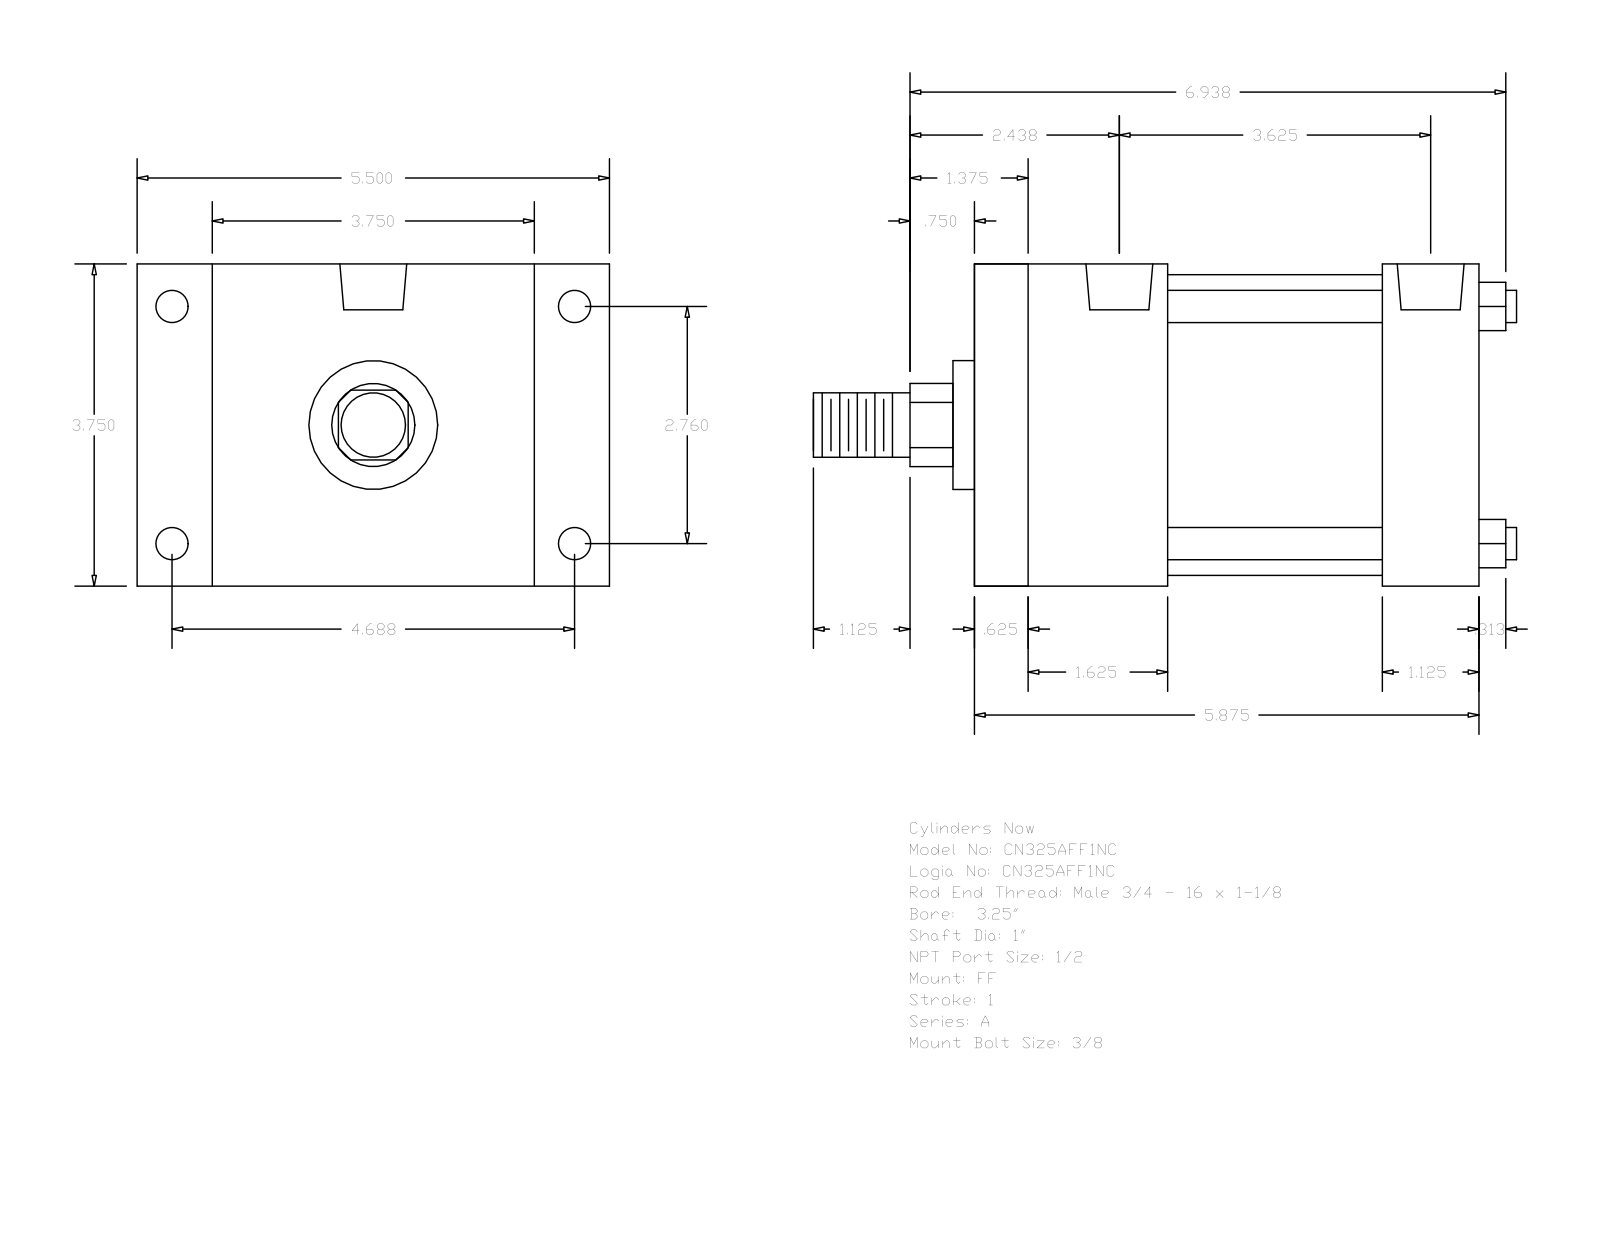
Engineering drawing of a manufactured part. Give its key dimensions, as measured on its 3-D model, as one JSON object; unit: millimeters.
{"part_name": "A_FF__0325_1", "step_written_by": "GSSL Pune (CONFIG_CONTROL_DESIGN)", "units": "millimeters", "bodies": {"solids": 0, "faces": 92, "planar": 64, "cylindrical": 28, "other": 0}, "overall_size": [207.96, 139.7, 95.25], "round_holes": [[8.73, 4], [9.53, 4], [19.77, 2]], "round_bosses_or_shafts": [[9.53, 4], [88.9, 1], [38.1, 1], [25.4, 1], [19.05, 1]], "partial_cylinders_radius": [[12.29, 1]], "face_to_face_distances": [95.24, 149.23, 15.87, 133.36, 63.5, 22.23, 117.47, 57.15, 120.65, 41.28], "hole_center_spacings": [3.18, 70.1, 85.72, 88.9, 119.06, 138.16, 92.08]}
